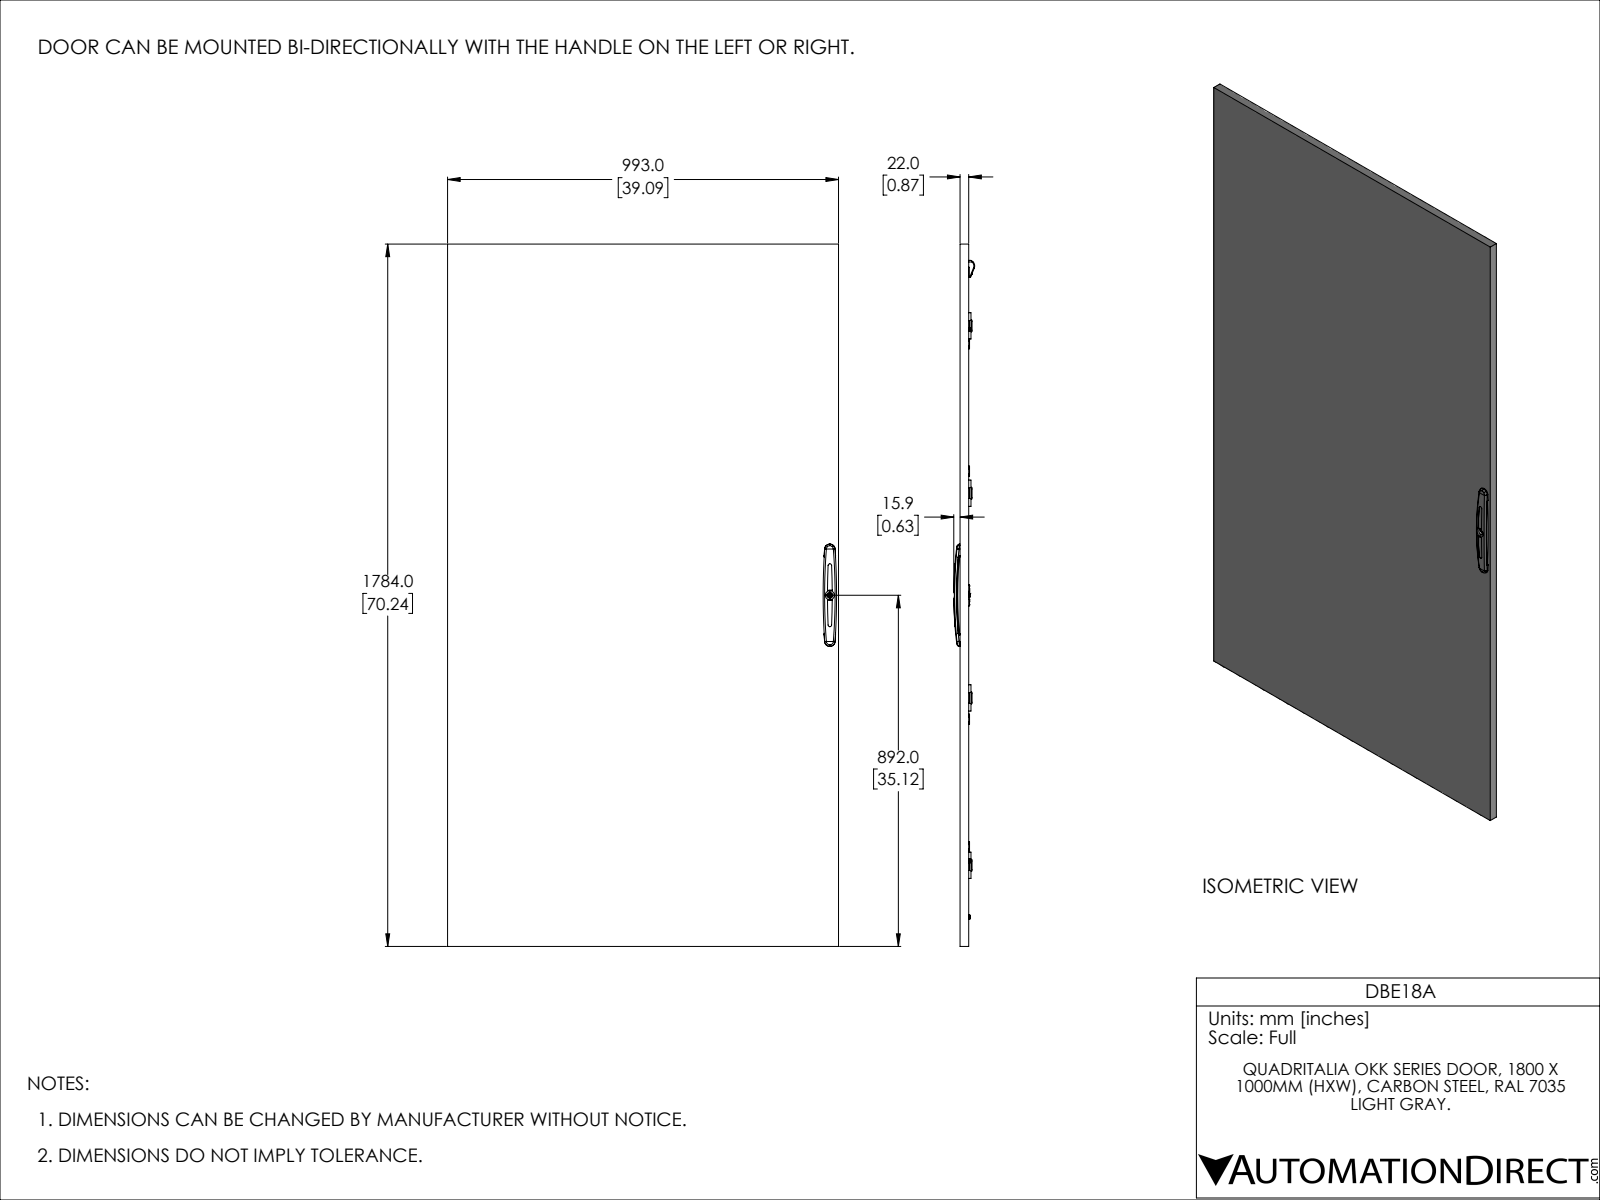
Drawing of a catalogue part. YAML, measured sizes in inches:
part_name: "DBE18A"
step_written_by: "SolidWorks 2021 (CONFIG_CONTROL_DESIGN)"
units: inches
bodies: {solids: 87, faces: 3315, planar: 1599, cylindrical: 1185, other: 531}
overall_size: [70.236, 39.094, 2.091]
volume: 306.8
surface_area: 7634
round_holes:
  - {diameter: 0.167, count: 152}
  - {diameter: 0.354, count: 20}
  - {diameter: 0.01, count: 8}
  - {diameter: 0.197, count: 8}
  - {diameter: 0.194, count: 6}
  - {diameter: 0.194, count: 4}
  - {diameter: 0.244, count: 4}
  - {diameter: 0.276, count: 4}
  - {diameter: 0.205, count: 3}
  - {diameter: 0.134, count: 2}
  - {diameter: 0.169, count: 2}
  - {diameter: 0.173, count: 2}
round_bosses_or_shafts:
  - {diameter: 0.276, count: 23}
  - {diameter: 0.236, count: 19}
  - {diameter: 0.283, count: 10}
  - {diameter: 0.193, count: 8}
  - {diameter: 0.472, count: 2}
  - {diameter: 0.394, count: 2}
  - {diameter: 0.315, count: 2}
  - {diameter: 0.157, count: 2}
partial_cylinders:
  - {radius: 0.012, count: 74}
  - {radius: 0.039, count: 70}
  - {radius: 0.059, count: 36}
  - {radius: 0.02, count: 33}
  - {radius: 0.098, count: 28}
  - {radius: 0.177, count: 16}
  - {radius: 0.079, count: 15}
  - {radius: 0.008, count: 10}
face_to_face_distances: [0.079, 0.059, 0.728, 0.787, 0.669, 33.858, 0.866, 0.138, 0.807, 39.016]
hole_center_spacings: [0.984, 1.969, 2.953, 3.937, 4.921, 5.906, 6.89, 7.874]
